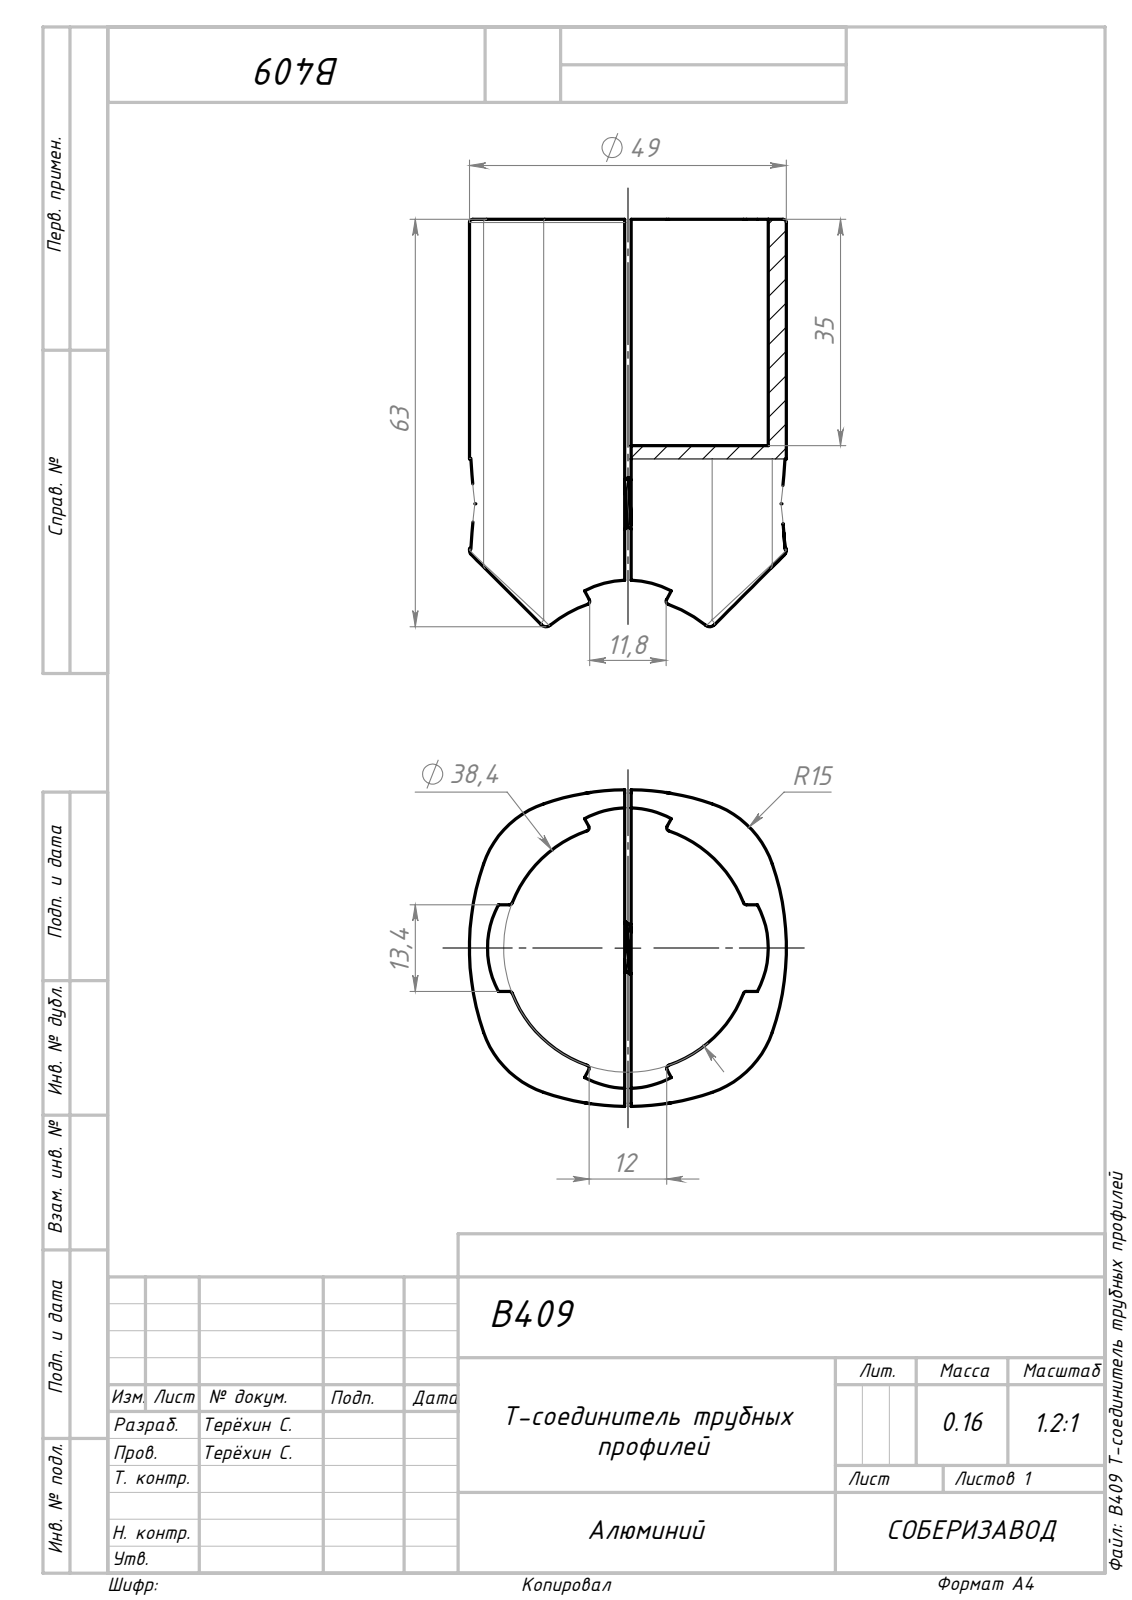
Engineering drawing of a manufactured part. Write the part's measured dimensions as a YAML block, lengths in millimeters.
part_name: "B409 Т-соединитель трубных профилей"
step_written_by: "SolidWorks 2022 (AUTOMOTIVE_DESIGN)"
units: millimeters
bodies: {solids: 4, faces: 353, planar: 98, cylindrical: 143, other: 112}
overall_size: [63.02, 49, 48.99]
volume: 59133
surface_area: 28631
round_holes:
  - {diameter: 7.2, count: 1}
  - {diameter: 8.5, count: 1}
round_bosses_or_shafts:
  - {diameter: 12.3, count: 1}
  - {diameter: 8, count: 1}
partial_cylinders:
  - {radius: 0.5, count: 30}
  - {radius: 1, count: 6}
  - {radius: 14.2, count: 5}
  - {radius: 12, count: 4}
  - {radius: 15, count: 4}
  - {radius: 37, count: 4}
  - {radius: 40, count: 4}
  - {radius: 19, count: 1}
face_to_face_distances: [1, 35, 12.8, 12, 15.89, 3.09, 7, 18, 13, 6]
